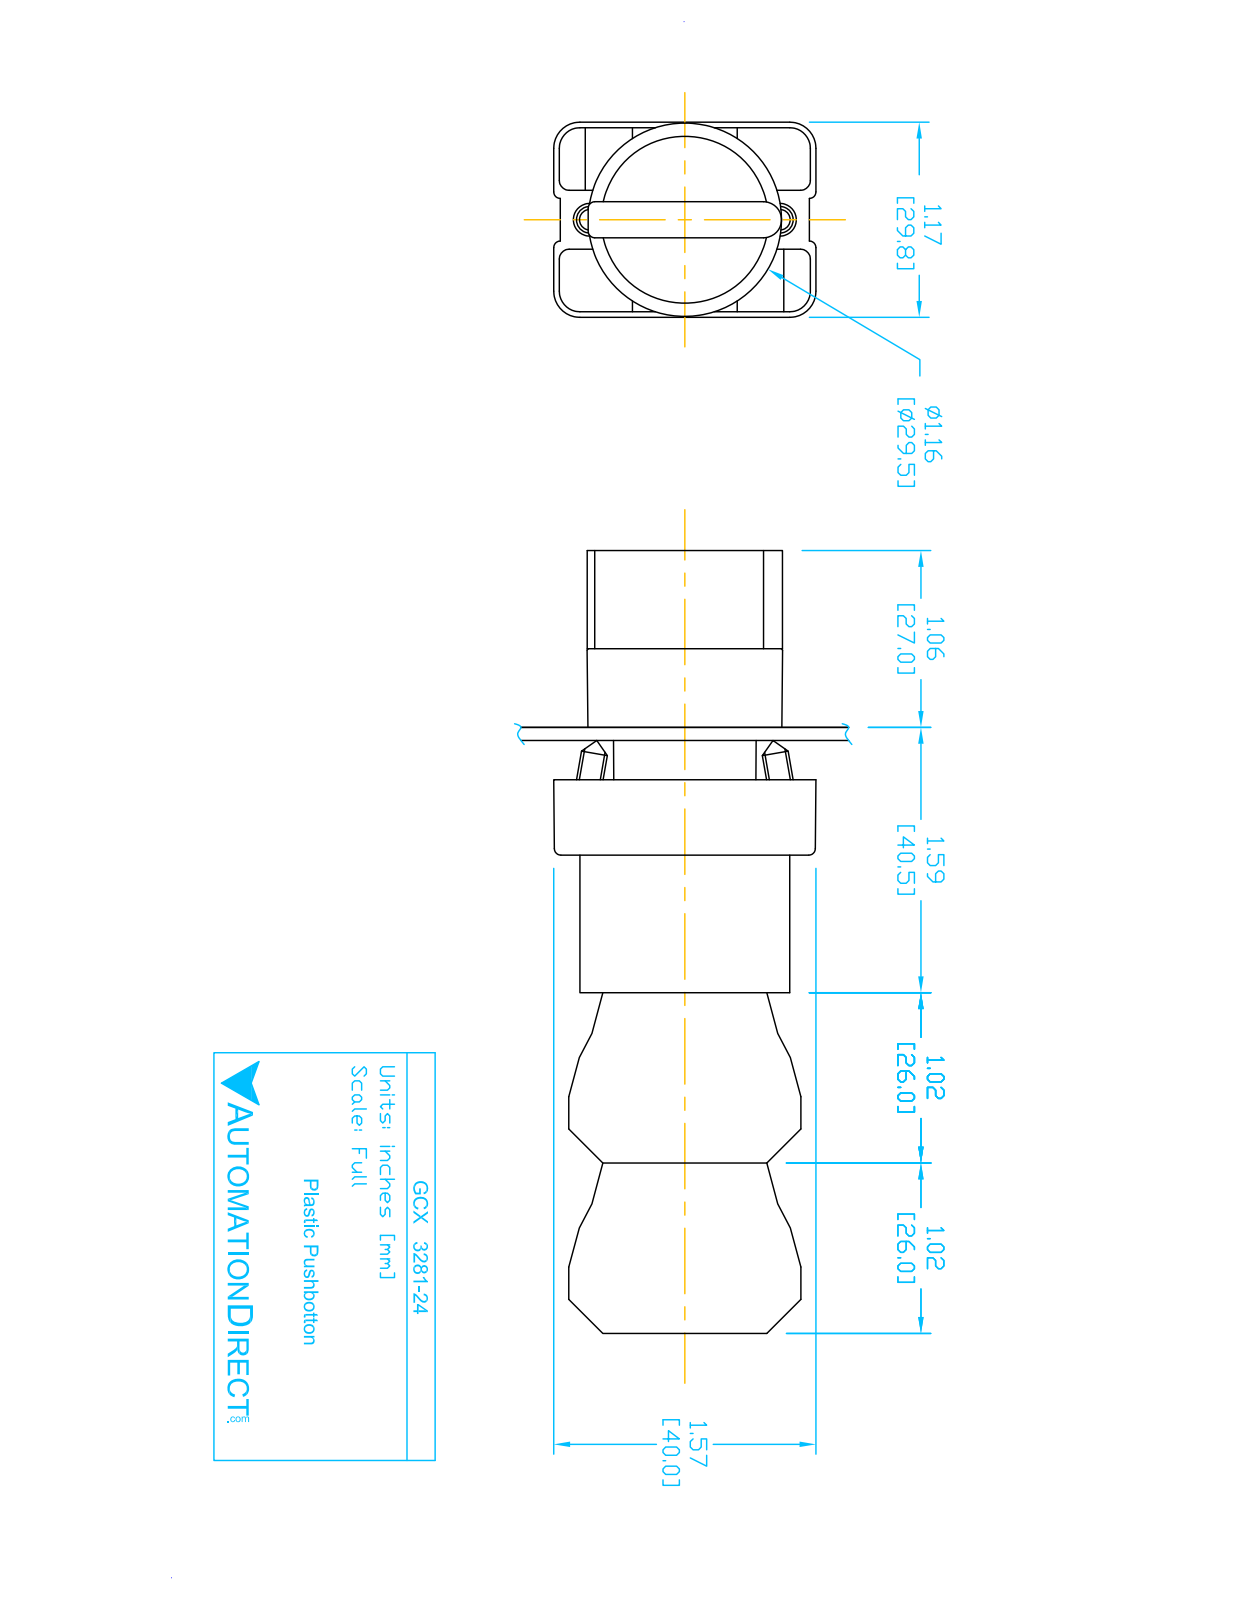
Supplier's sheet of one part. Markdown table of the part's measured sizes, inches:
| quantity | value |
| --- | --- |
| part name | ecx1030; ecx1040; ECX1050; GCX3281-24 (+2 more) |
| STEP written by | SolidWorks 2016 (AUTOMOTIVE_DESIGN) |
| units | inches |
| bodies | 11 solids, 724 faces (488 planar, 193 cylindrical, 43 other) |
| overall size | 4.677 × 1.581 × 1.177 |
| volume | 4.751 in³ |
| surface area | 59.22 in² |
| round holes (diameter × count) | 0.079 × 4, 0.087 × 2, 0.124 × 2, 0.13 × 2, 0.197 × 1, 0.469 × 1, 0.878 × 1, 0.888 × 1, 1.024 × 1 |
| round bosses / shafts (diameter × count) | 0.157 × 4, 1.175 × 1, 1.004 × 1, 0.945 × 1, 0.856 × 1, 0.78 × 1, 0.504 × 1 |
| partial cylindrical surfaces (radius × count) | 0.059 × 24, 0.041 × 12, 0.124 × 12, 0.157 × 12, 0.039 × 9, 0.02 × 2, 0.063 × 2, 0.079 × 2 |
| main face-to-face distances | 0.579, 0.593, 1.024, 1.171, 0.014, 0.827, 1.85, 3.043, 2.02, 1.193 |
| hole center spacings | 0.236, 1.003, 0.974, 0.472, 0.539, 0.544, 1.083, 0.484 |
